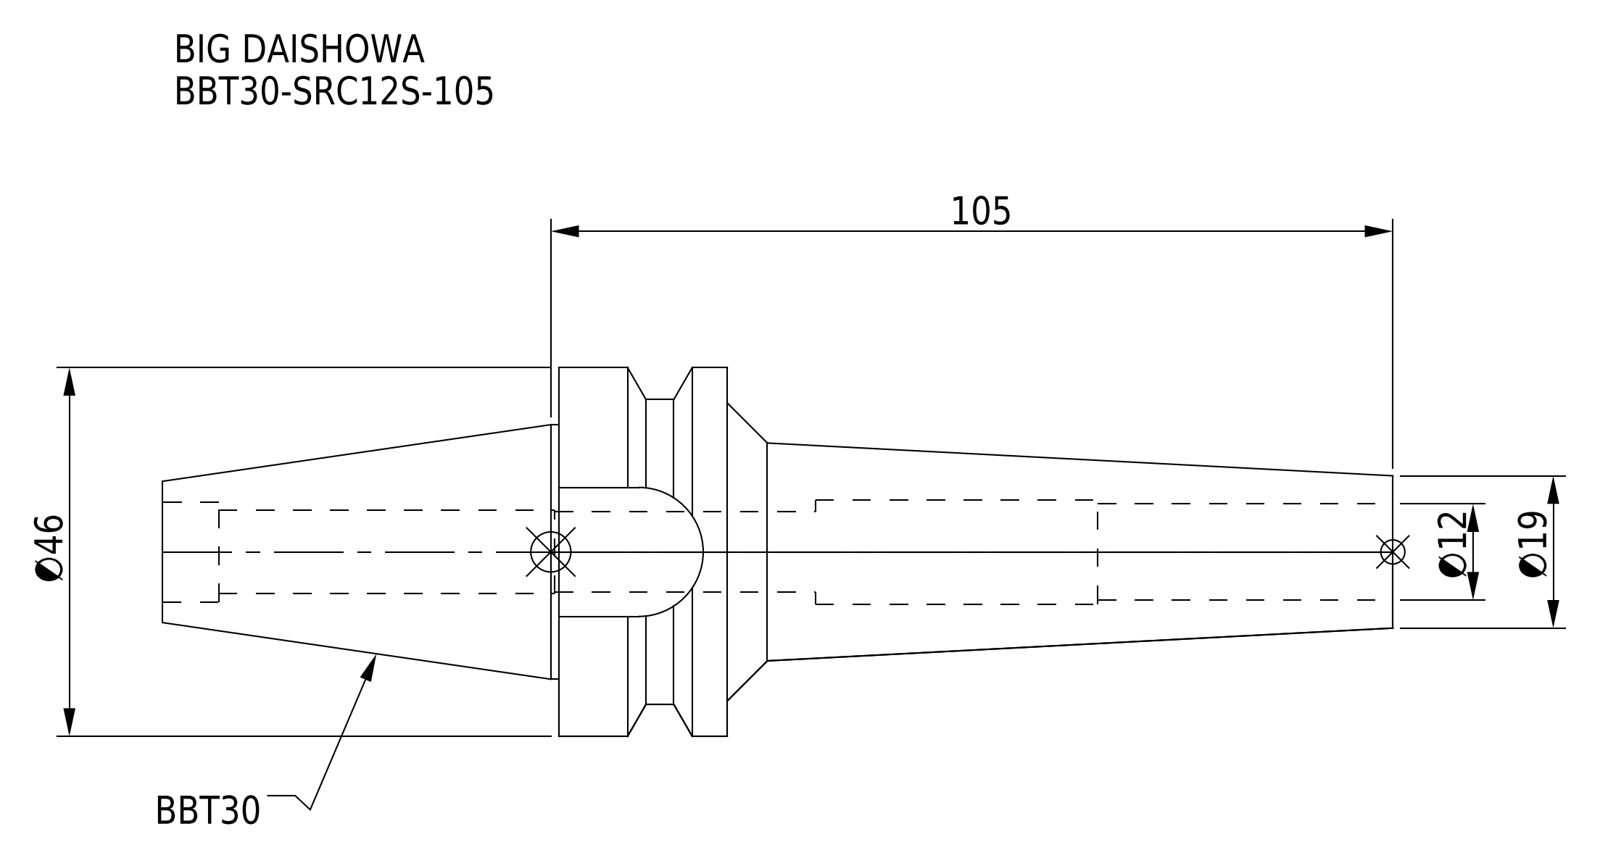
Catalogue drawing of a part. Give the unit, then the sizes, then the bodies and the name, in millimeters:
Units: millimetres
Overall size (bounding box): 153.4 × 46 × 46
Round holes (diameter × count): ⌀10 ×1, ⌀10.4 ×1, ⌀12 ×1, ⌀12.5 ×1, ⌀13 ×1
Round bosses / shafts (diameter × count): ⌀46 ×1, ⌀31.75 ×1
Partial cylindrical surfaces — rounded edges, fillets, slot ends (radius × count): R8.05 ×1, R19 ×1
Main face-to-face distances: 21, 32.6, 83, 104, 153.4, 70.4, 49.4, 16.1, 72, 11
Volume: 75 119 mm³ · Surface area: 21 180 mm²
Bodies: 1 solid, 46 faces (14 planar, 22 cylindrical, 10 other)
Part name (STEP PRODUCT): BBT30-SRC12S-105
STEP written by: CREO PARAMETRIC BY PTC INC, 2016380 (AUTOMOTIVE_DESIGN)
